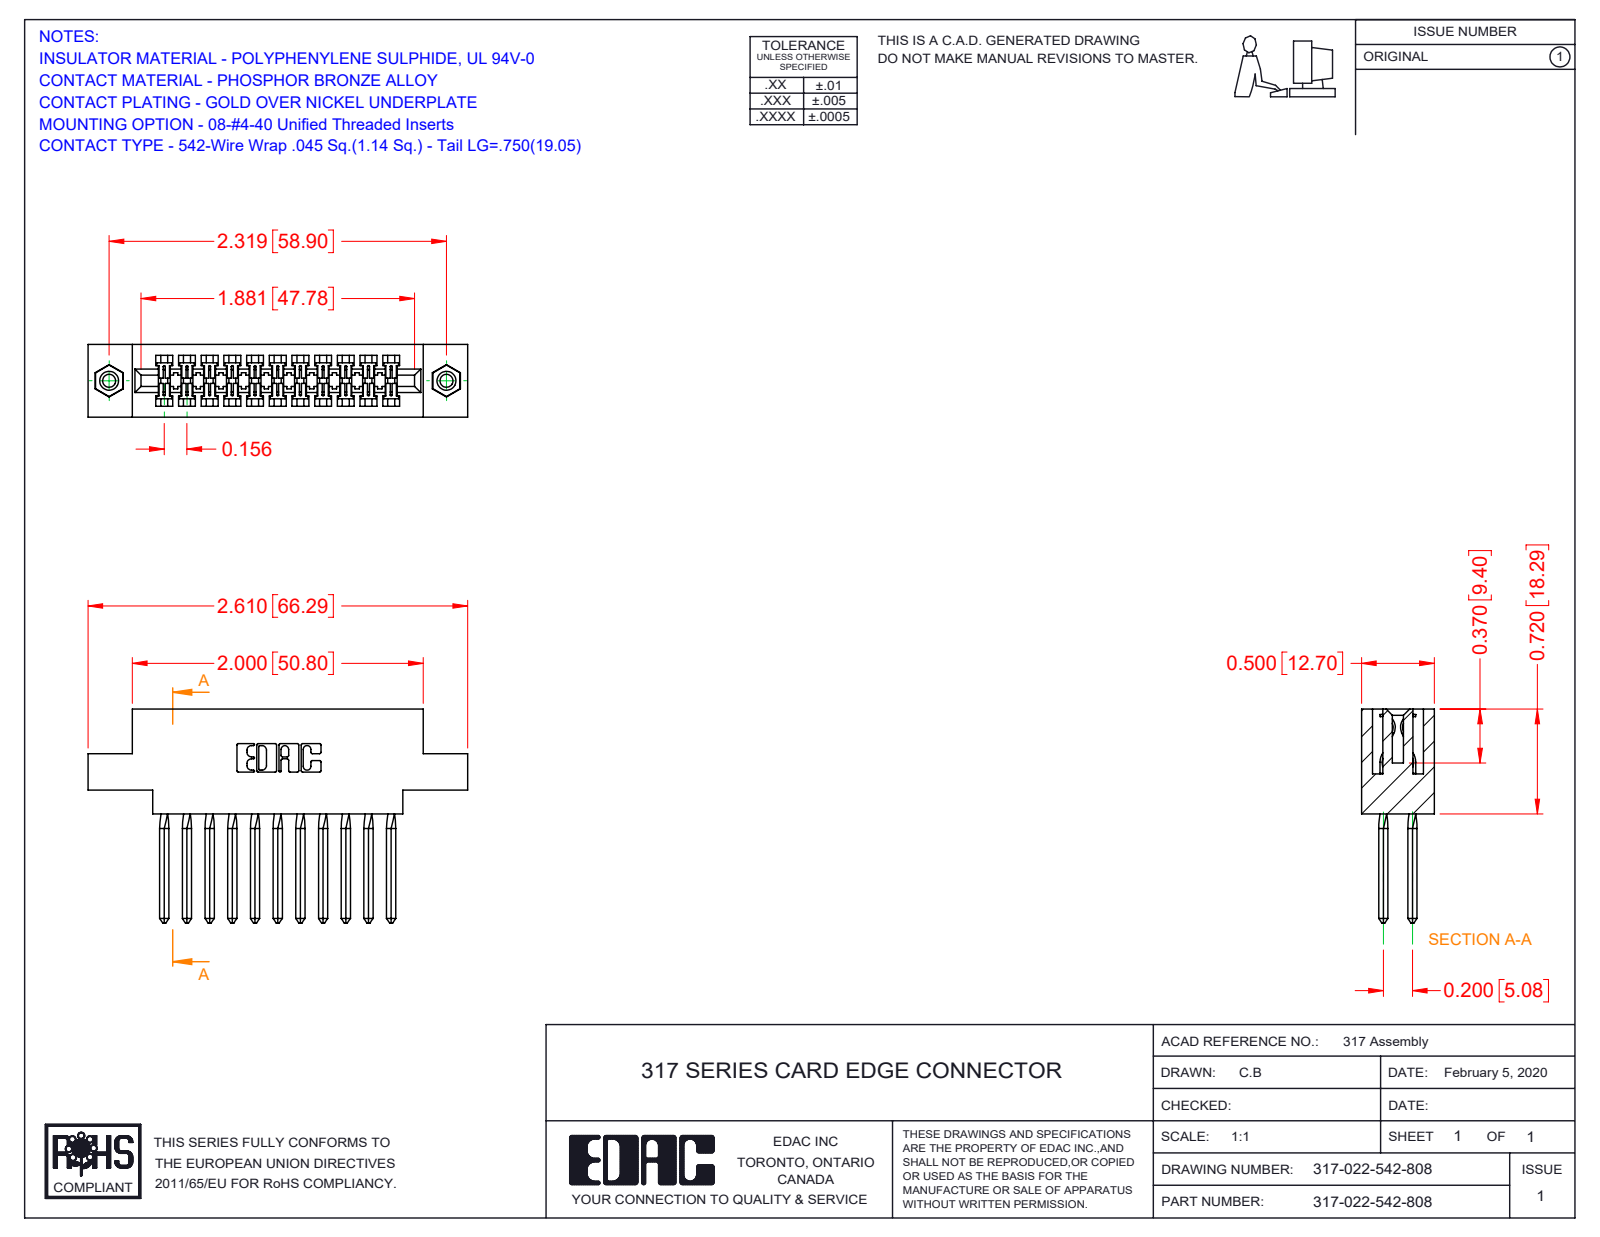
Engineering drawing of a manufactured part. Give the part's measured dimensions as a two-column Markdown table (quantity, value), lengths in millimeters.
| quantity | value |
| --- | --- |
| part name | 317 Part_.156 Dia - TI; 345-250-001_345-250-003-102; 317-290-003_542; 317-022-542-878 |
| STEP written by | SolidWorks 2016 (CONFIG_CONTROL_DESIGN) |
| units | millimeters |
| bodies | 25 solids, 1416 faces (1102 planar, 210 cylindrical, 104 other) |
| overall size | 66.3 × 37.3 × 12.7 |
| volume | 9 870 mm³ |
| surface area | 12 750 mm² |
| round holes (diameter × count) | 2.3 × 2, 3.2 × 2, 4 × 2 |
| round bosses / shafts (diameter × count) | 3.9 × 2 |
| partial cylindrical surfaces (radius × count) | 0.2 × 44, 0.3 × 22, 0.2 × 6, 0.8 × 6, 0.7 × 3, 1.9 × 2, 2.3 × 2, 2.5 × 2 |
| main face-to-face distances | 12.7, 1.9, 10.8, 2.8, 2.9, 5.6, 8.9, 3.5, 5.1, 4 |
| hole center spacings | 58.9 |
